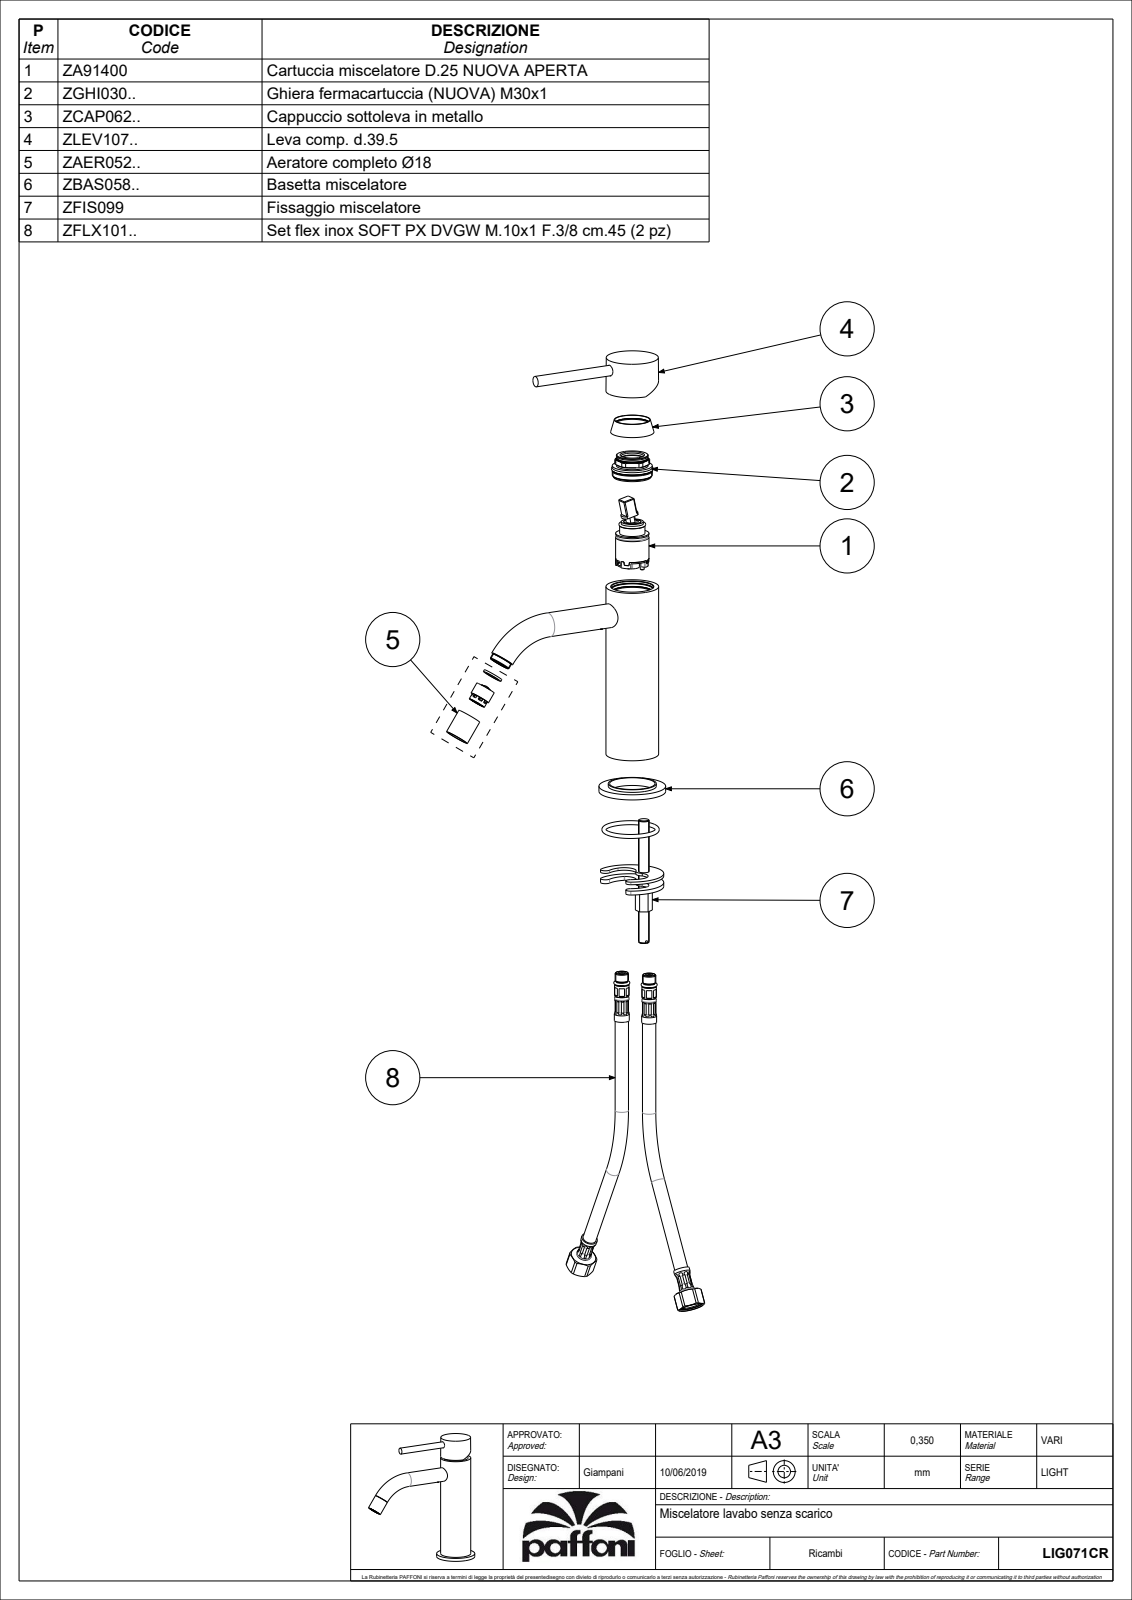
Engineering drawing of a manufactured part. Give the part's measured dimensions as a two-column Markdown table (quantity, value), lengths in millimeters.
| quantity | value |
| --- | --- |
| part name | LIG071CR |
| STEP written by | CREO PARAMETRIC BY PTC INC, 2020044 (CONFIG_CONTROL_DESIGN) |
| units | millimeters |
| bodies | 1 solid, 1124 faces (268 planar, 541 cylindrical, 315 other) |
| overall size | 162.15 × 155.45 × 50 |
| volume | 145 501 mm³ |
| surface area | 72 730 mm² |
| round holes (diameter × count) | 0.5 × 51, 11 × 4, 10 × 3, 5 × 2, 9 × 2, 12 × 2, 14 × 2, 3 × 1, 6.5 × 1, 6.8 × 1, 8 × 1, 12.5 × 1 |
| round bosses / shafts (diameter × count) | 18 × 2, 50 × 1, 43 × 1, 39.5 × 1, 36 × 1, 25 × 1, 22.6 × 1, 19 × 1 |
| partial cylindrical surfaces (radius × count) | 0.5 × 56, 1 × 18, 0.7 × 10, 0.8 × 6, 0.6 × 4, 0.65 × 4, 0.85 × 4, 2 × 4 |
| main face-to-face distances | 4, 2, 10, 14, 159.15, 155.15, 145.15, 12, 130, 1 |
| hole center spacings | 1.5, 3.35, 3, 4.74, 2.12, 3.36, 2.13, 4.24 |
